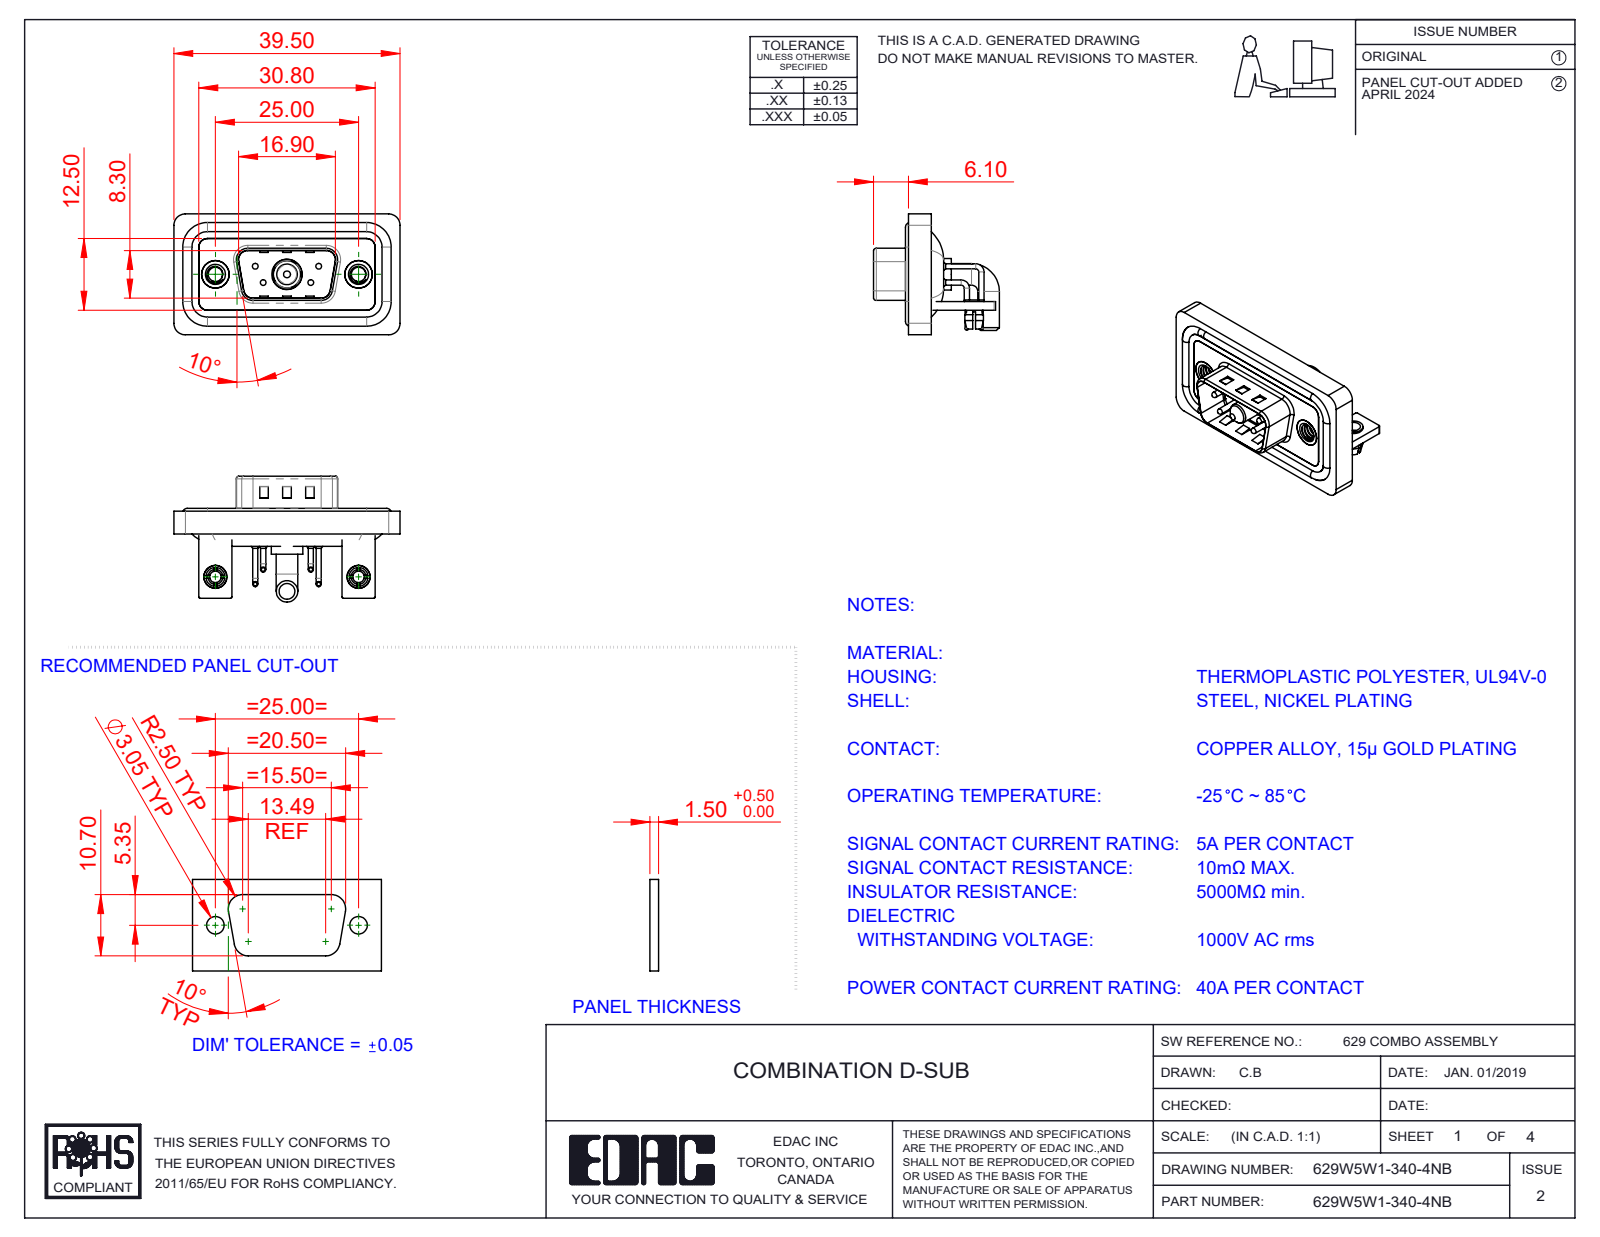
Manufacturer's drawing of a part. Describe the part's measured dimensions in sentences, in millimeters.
The part is named "629Combo Housing_5W1; Power Pin_40A RA; 629W5W1-340-4NB; 629Combo Contact Row 1 (+7 more)". Its 3-D file was written by "SolidWorks 2023 (CONFIG_CONTROL_DESIGN)". It is 17 solids with 1024 faces: 479 planar, 395 cylindrical and 150 other. Overall it measures 39.5 by 21.98 by 21.1 millimeters. Its volume is 4 857 cubic millimeters and its surface area 8 006 square millimeters. Round holes: 6 of diameter 2, 4 of diameter 0.75, 4 of diameter 1.6, 4 of diameter 2.5, 2 of diameter 3.2, 2 of diameter 4, 2 of diameter 4.8, 2 of diameter 5, 1 of diameter 4.85, 1 of diameter 5.3. Round bosses or shafts: 8 of diameter 0.9, 4 of diameter 1.6, 4 of diameter 1.5, 4 of diameter 1, 4 of diameter 0.65, 2 of diameter 4.9, 2 of diameter 4, 2 of diameter 3.75. Partial cylindrical surfaces (rounded edges, fillets, slot ends): 19 of radius 2, 18 of radius 1.5, 16 of radius 0.25, 9 of radius 0.5, 8 of radius 1.6, 4 of radius 0.6, 4 of radius 0.65, 4 of radius 0.9. The main face-to-face distances are 0.4, 1.5, 0.8, 2.9, 1.1, 2.1, 1.2, 1.6, 2.5, 3.7. The hole center spacings are 3.16, 5.72, 7.1, 12.5, 18.1, 25, 4.39, 4.4.
